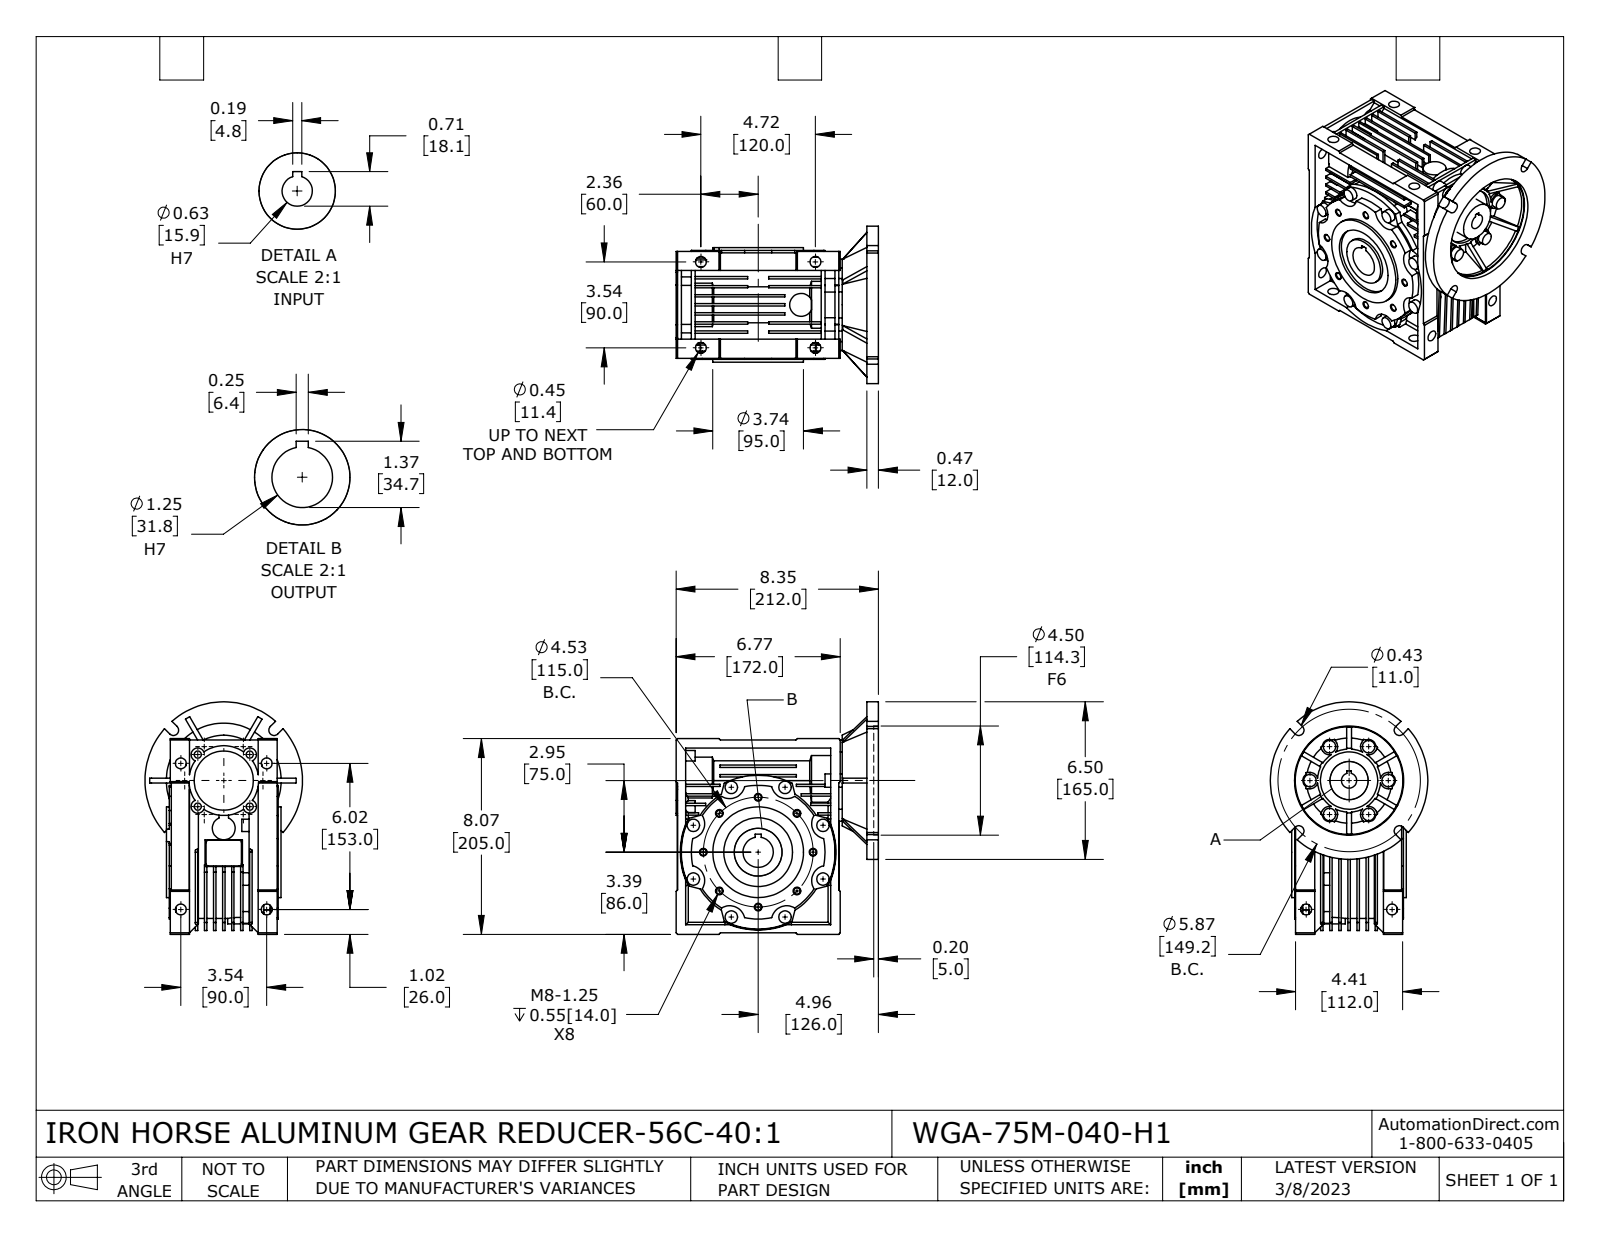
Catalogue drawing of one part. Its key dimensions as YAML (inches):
part_name: "WGA-75M-040-H1"
step_written_by: "SolidWorks 2021 (CONFIG_CONTROL_DESIGN)"
units: inches
bodies: {solids: 4, faces: 1179, planar: 675, cylindrical: 386, other: 118}
overall_size: [9.587, 8.346, 6.496]
volume: 180.8
surface_area: 779.6
round_holes:
  - {diameter: 0.262, count: 8}
  - {diameter: 0.448, count: 8}
  - {diameter: 0.293, count: 4}
  - {diameter: 0.625, count: 1}
  - {diameter: 0.65, count: 1}
  - {diameter: 1, count: 1}
  - {diameter: 1.25, count: 1}
  - {diameter: 1.535, count: 1}
  - {diameter: 1.654, count: 1}
  - {diameter: 1.969, count: 1}
  - {diameter: 2.441, count: 1}
  - {diameter: 2.677, count: 1}
round_bosses_or_shafts:
  - {diameter: 0.512, count: 14}
  - {diameter: 0.945, count: 3}
  - {diameter: 6.496, count: 1}
  - {diameter: 5.509, count: 1}
  - {diameter: 5.465, count: 1}
  - {diameter: 3.74, count: 1}
  - {diameter: 2.992, count: 1}
  - {diameter: 2.795, count: 1}
partial_cylinders:
  - {radius: 0.276, count: 10}
  - {radius: 0.63, count: 8}
  - {radius: 0.295, count: 6}
  - {radius: 0.335, count: 6}
  - {radius: 0.098, count: 4}
  - {radius: 0.217, count: 4}
  - {radius: 1.299, count: 1}
  - {radius: 1.417, count: 1}
face_to_face_distances: [0.374, 0.098, 0.472, 0.748, 0.276, 1.122, 1.496, 0.394, 0.65, 0.846]
hole_center_spacings: [2.264, 1.733, 3.202, 4.183, 1.515, 2.143, 3.543, 4.528]
